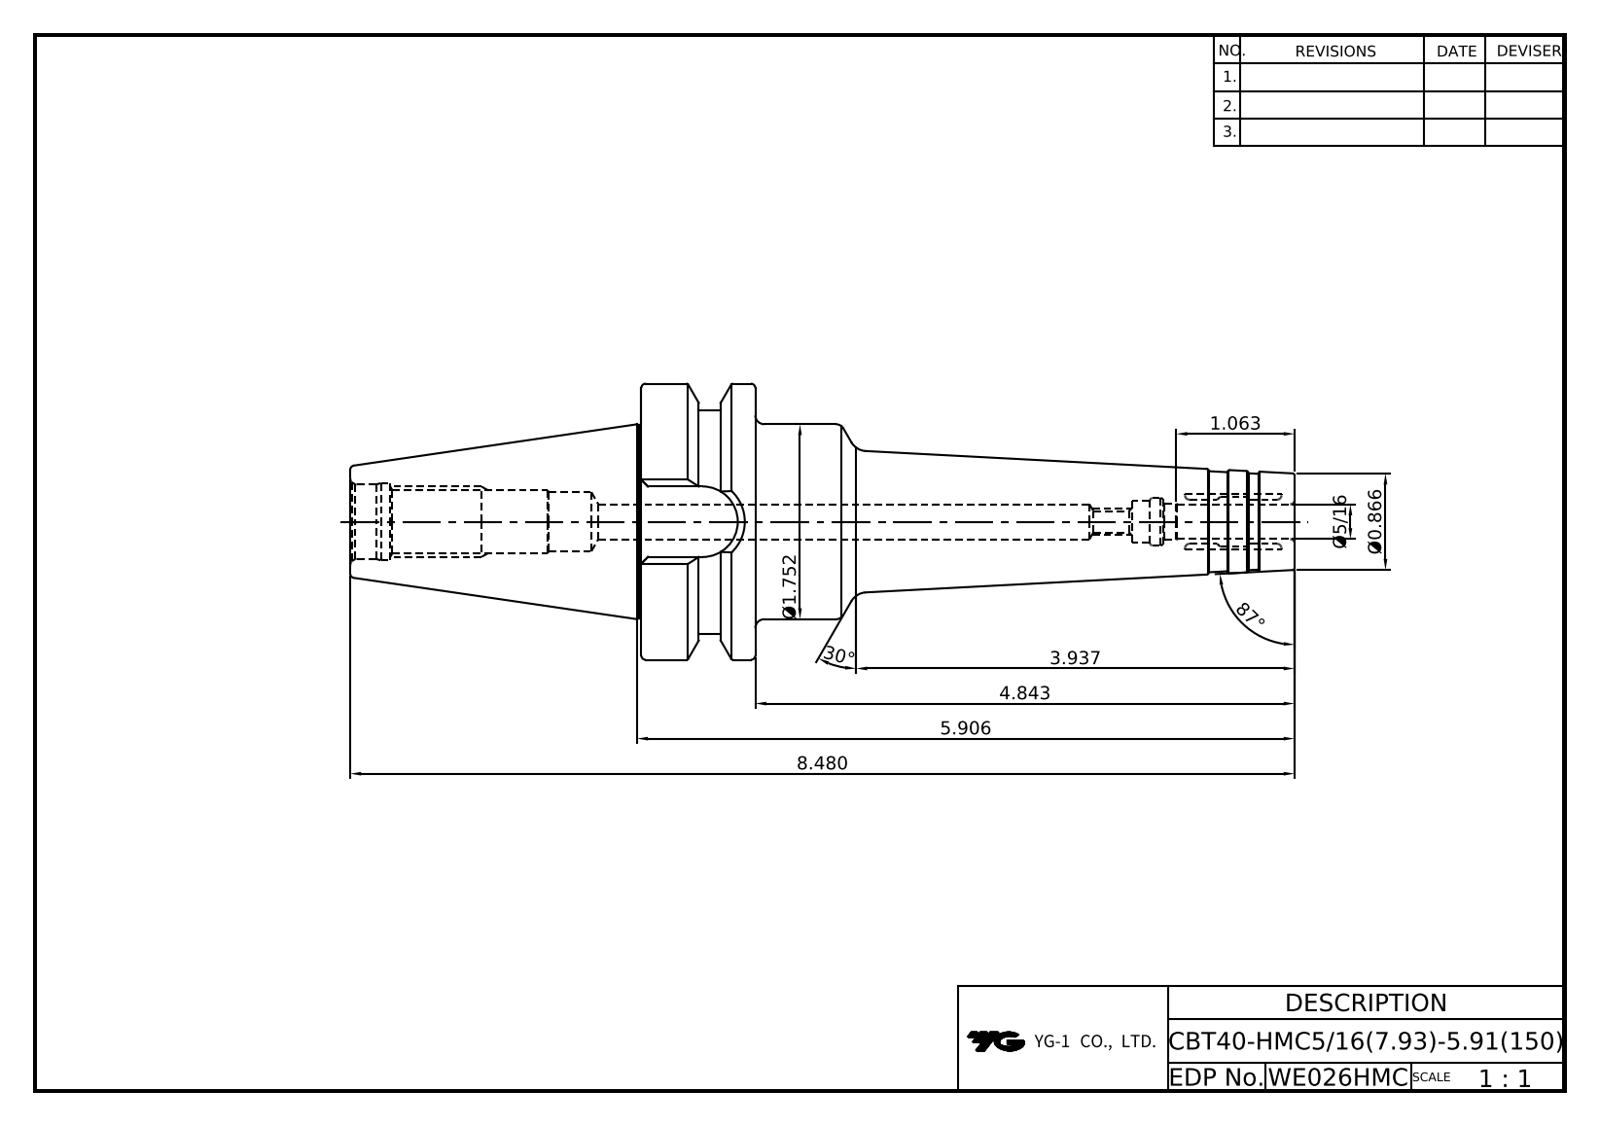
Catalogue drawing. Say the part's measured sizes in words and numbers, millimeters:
The part is named "LO-CBT40-HMC7.9375-150". Its 3-D file was written by "Autodesk Inventor 2022 (AUTOMOTIVE_DESIGN)". It is 1 solid with 83 faces: 24 planar, 17 cylindrical and 42 other. Overall it measures 215.4 by 63 by 63 millimeters. Its volume is 209 376 cubic millimeters and its surface area 36 378 square millimeters. Round holes: 1 of diameter 4.92, 1 of diameter 7.94, 1 of diameter 8, 1 of diameter 8.54, 1 of diameter 13.5, 1 of diameter 13.84, 1 of diameter 17, 1 of diameter 17.6. Round bosses or shafts: 1 of diameter 63, 1 of diameter 51, 1 of diameter 44.5, 1 of diameter 44. Partial cylindrical surfaces (rounded edges, fillets, slot ends): 1 of radius 8.05. The main face-to-face distances are 26, 45.2, 149, 123, 18.1, 7.9, 130.9, 13.1, 5, 12.9.
